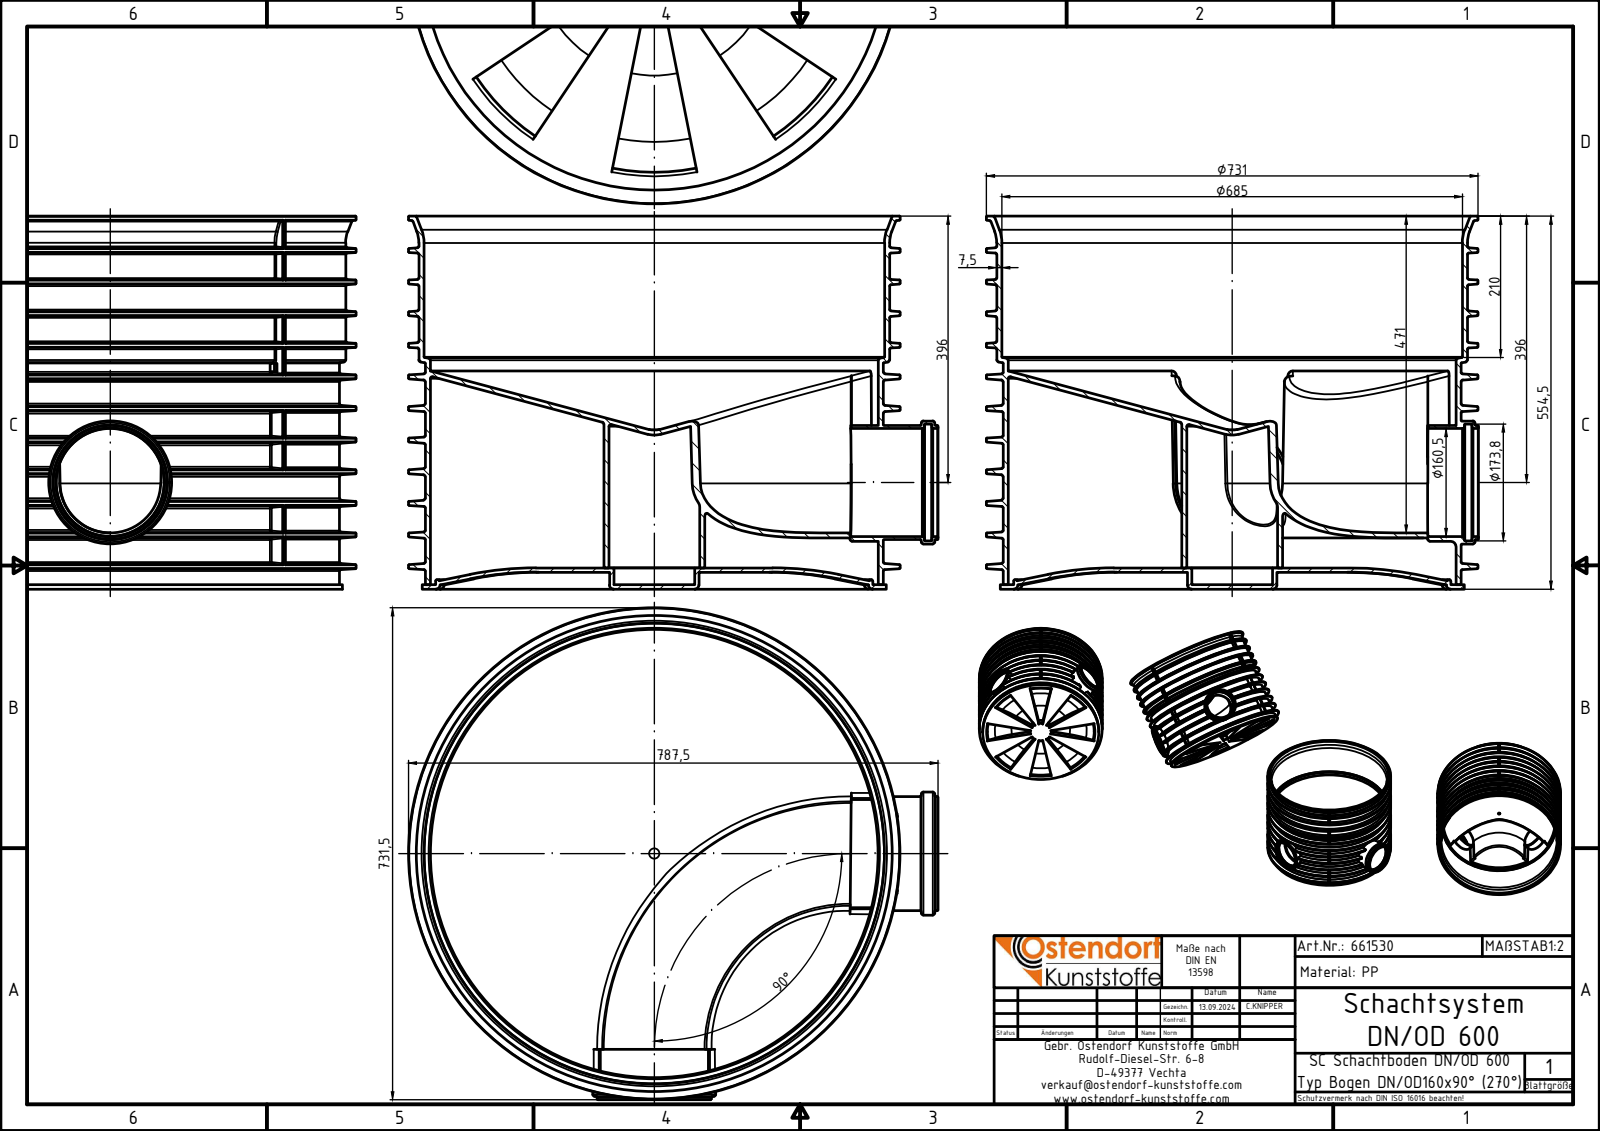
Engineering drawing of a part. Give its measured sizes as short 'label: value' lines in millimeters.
name: 661530z; 661530 Schacht DN600 Boden; 661530 Schachtboden DN600 Grundkörper
written by: Autodesk Inventor 2024 (AUTOMOTIVE_DESIGN)
unit: mm
bodies: 2 solids, 1548 faces (152 planar, 261 cylindrical, 1135 other)
size: 787.5 × 731.5 × 554.5
volume: 23 280 000 mm³; area: 5 539 000 mm²
holes: 2× ⌀160.5, 2× ⌀160.8, 2× ⌀173.8, 1× ⌀120, 1× ⌀135, 1× ⌀160.7, 1× ⌀169.8, 1× ⌀640, 1× ⌀666, 1× ⌀685
bosses: 2× ⌀182.8, 2× ⌀169.5, 1× ⌀731, 1× ⌀700, 1× ⌀690, 1× ⌀681, 1× ⌀650, 1× ⌀169.8
rounds: 16× R2, 8× R1, 4× R3, 2× R87.5, 1× R66.5, 1× R82.5, 1× R318.5
face distances: 6.5, 25, 31.5, 18.5, 554.5, 548, 529.5, 523, 7.5, 14
